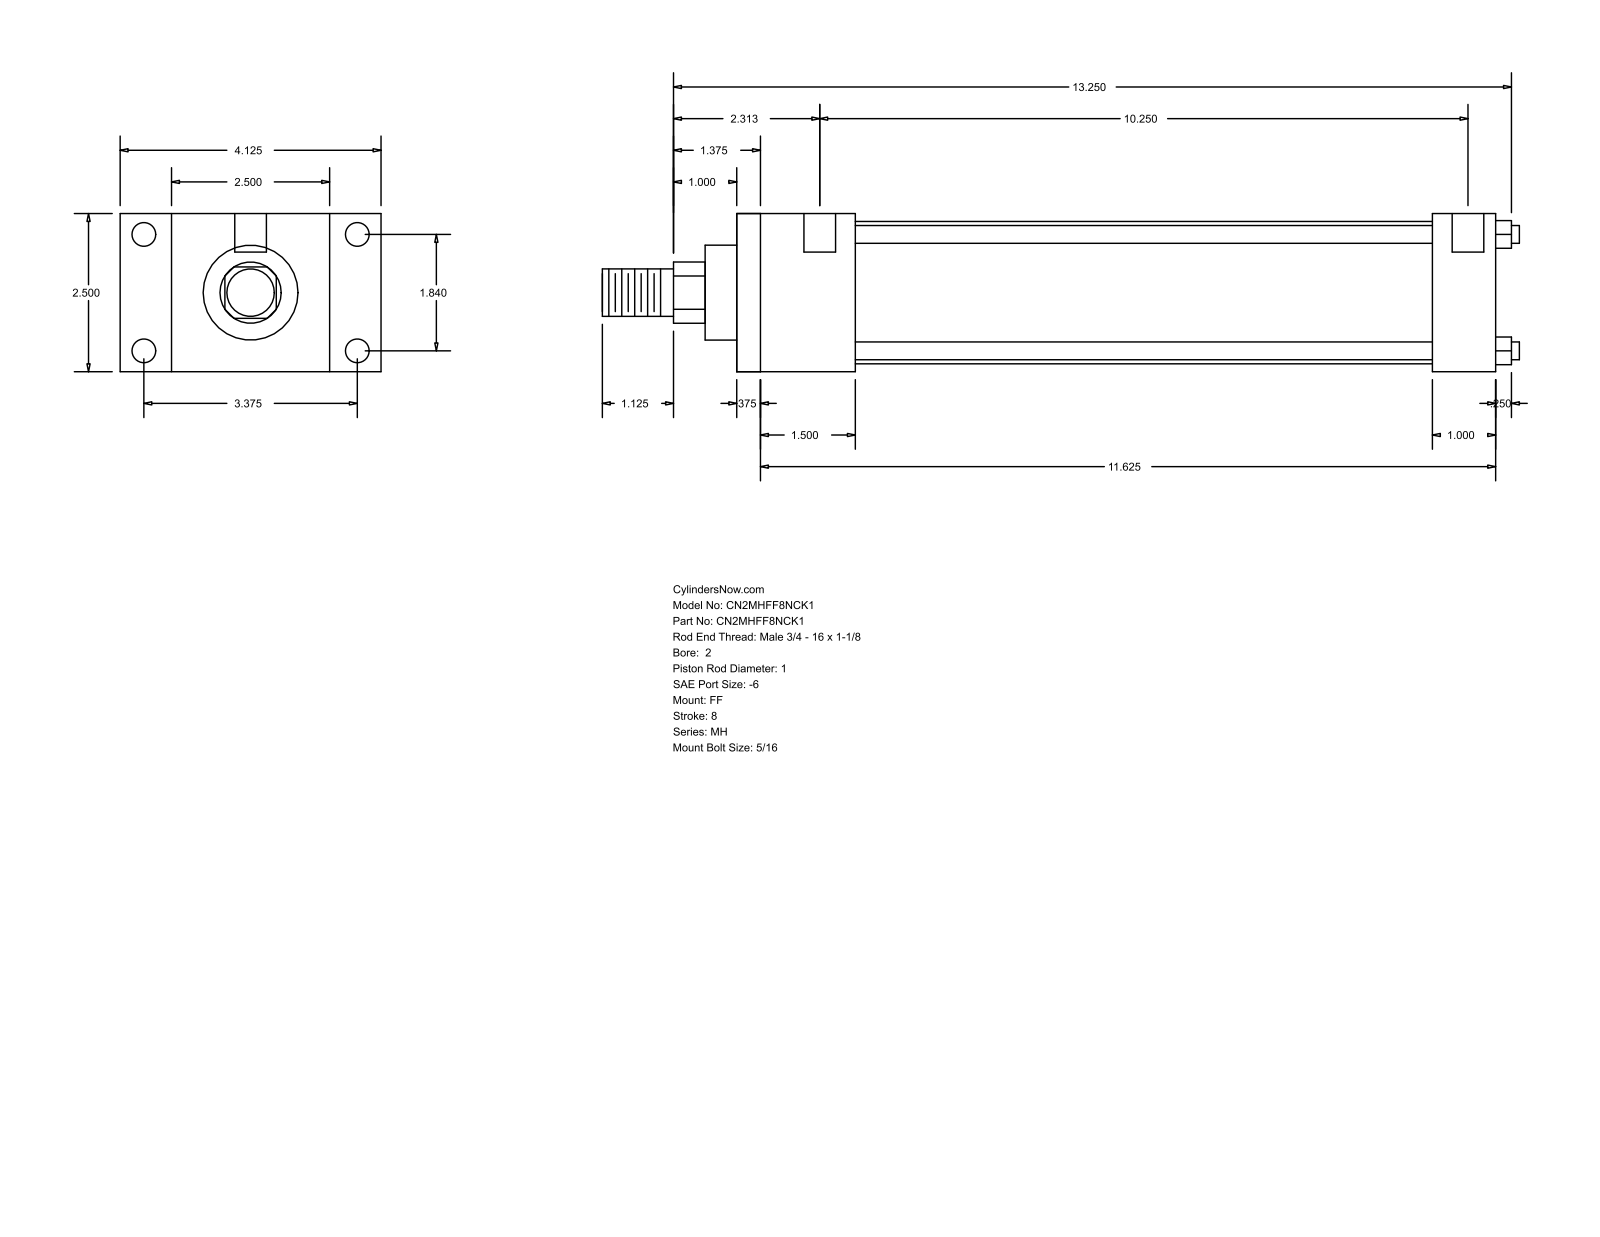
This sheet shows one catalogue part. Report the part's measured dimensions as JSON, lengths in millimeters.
{"part_name": "MH_FF__0200_1", "step_written_by": "GSSL Pune (CONFIG_CONTROL_DESIGN)", "units": "millimeters", "bodies": {"solids": 0, "faces": 92, "planar": 64, "cylindrical": 28, "other": 0}, "overall_size": [368.3, 104.78, 63.5], "round_holes": [[5.56, 4], [9.53, 4], [12.7, 2]], "round_bosses_or_shafts": [[7.14, 4], [57.15, 1], [38.1, 1], [25.4, 1], [19.05, 1]], "partial_cylinders_radius": [[12.29, 1]], "face_to_face_distances": [63.5, 304.8, 9.52, 295.28, 20.64, 25.4, 47.63, 279.4, 38.11, 269.88], "hole_center_spacings": [46.74, 85.72, 97.63, 268.28, 3.17, 4.76, 260.35, 263.52]}
